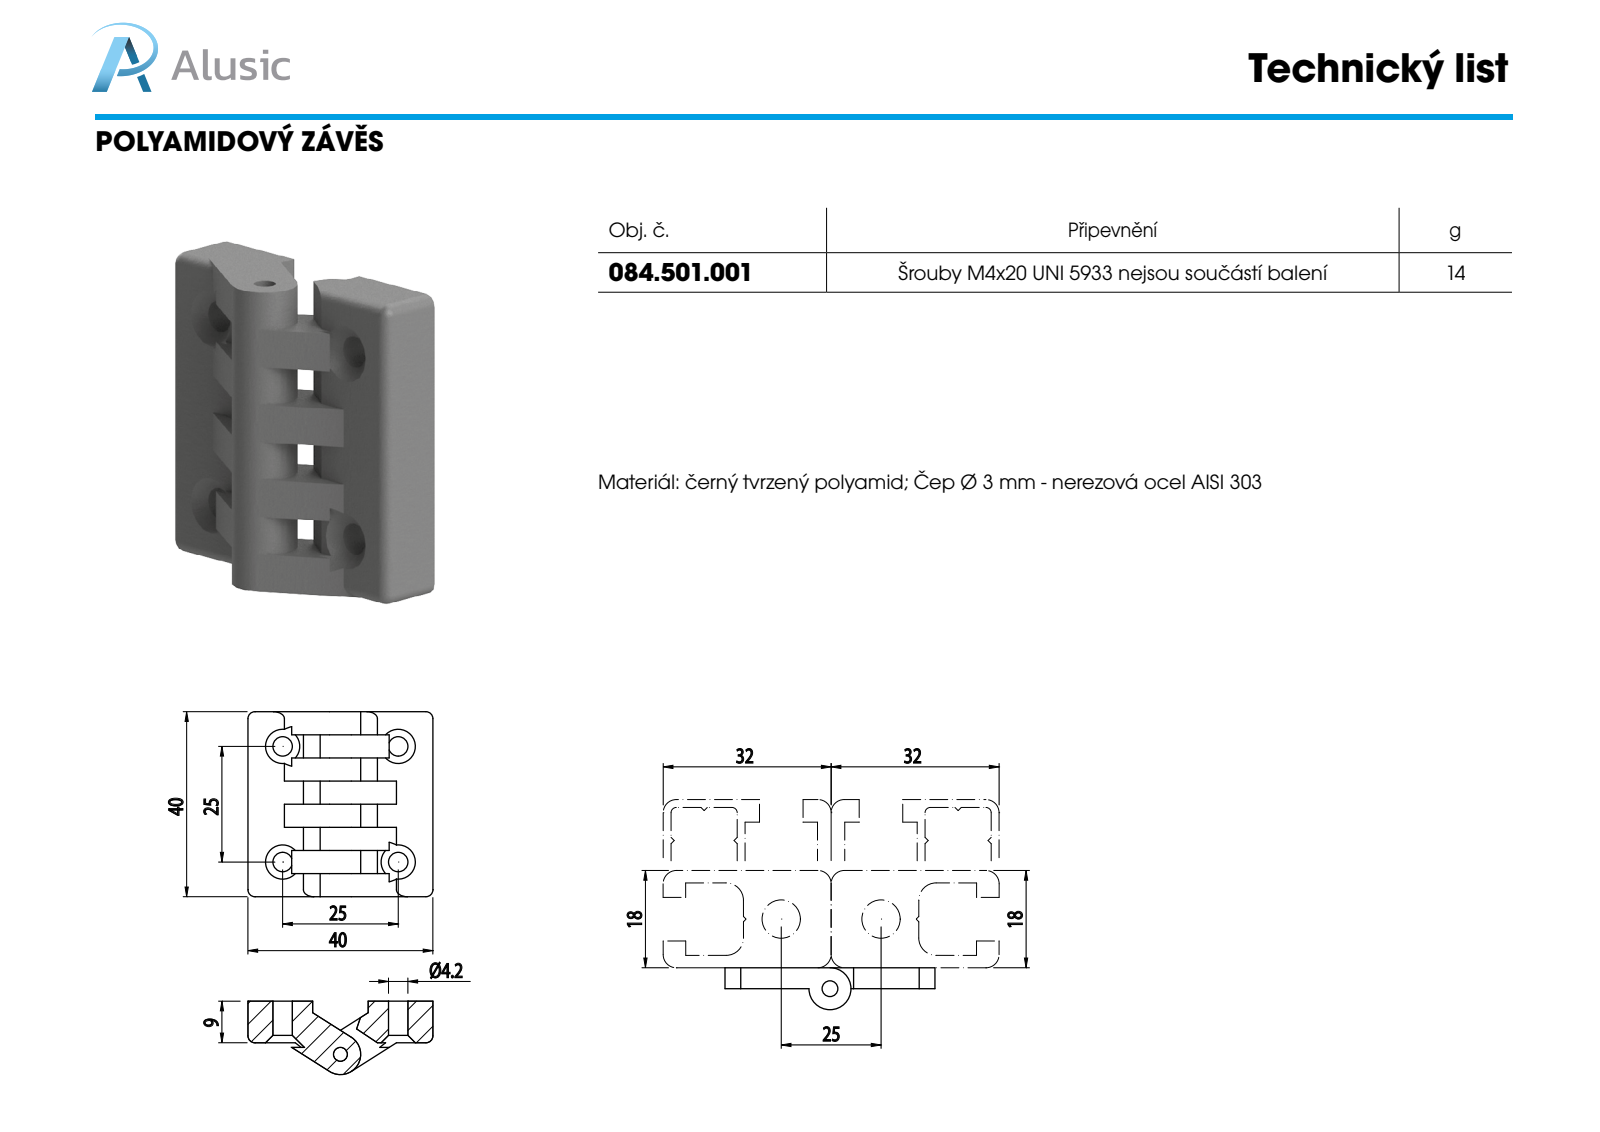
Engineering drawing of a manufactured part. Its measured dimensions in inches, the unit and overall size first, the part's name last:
Units: inches
Overall size (bounding box): 1.575 × 1.575 × 0.625
Round holes (diameter × count): ⌀0.165 ×4, ⌀0.118 ×1
Round bosses / shafts (diameter × count): ⌀0.345 ×1
Partial cylindrical surfaces — rounded edges, fillets, slot ends (radius × count): R0.059 ×8
Main face-to-face distances: 0.197, 0.394, 0.591, 0.787, 0.984, 1.575, 1.181, 0.354, 0.345, 1.378
Hole centre spacings: 0.984, 1.392
Volume: 0.827 in³ · Surface area: 11.28 in²
Bodies: 2 solids, 114 faces (60 planar, 42 cylindrical, 12 other)
Part name (STEP PRODUCT): 084.501.001
STEP written by: SolidWorks 2011 (CONFIG_CONTROL_DESIGN)
